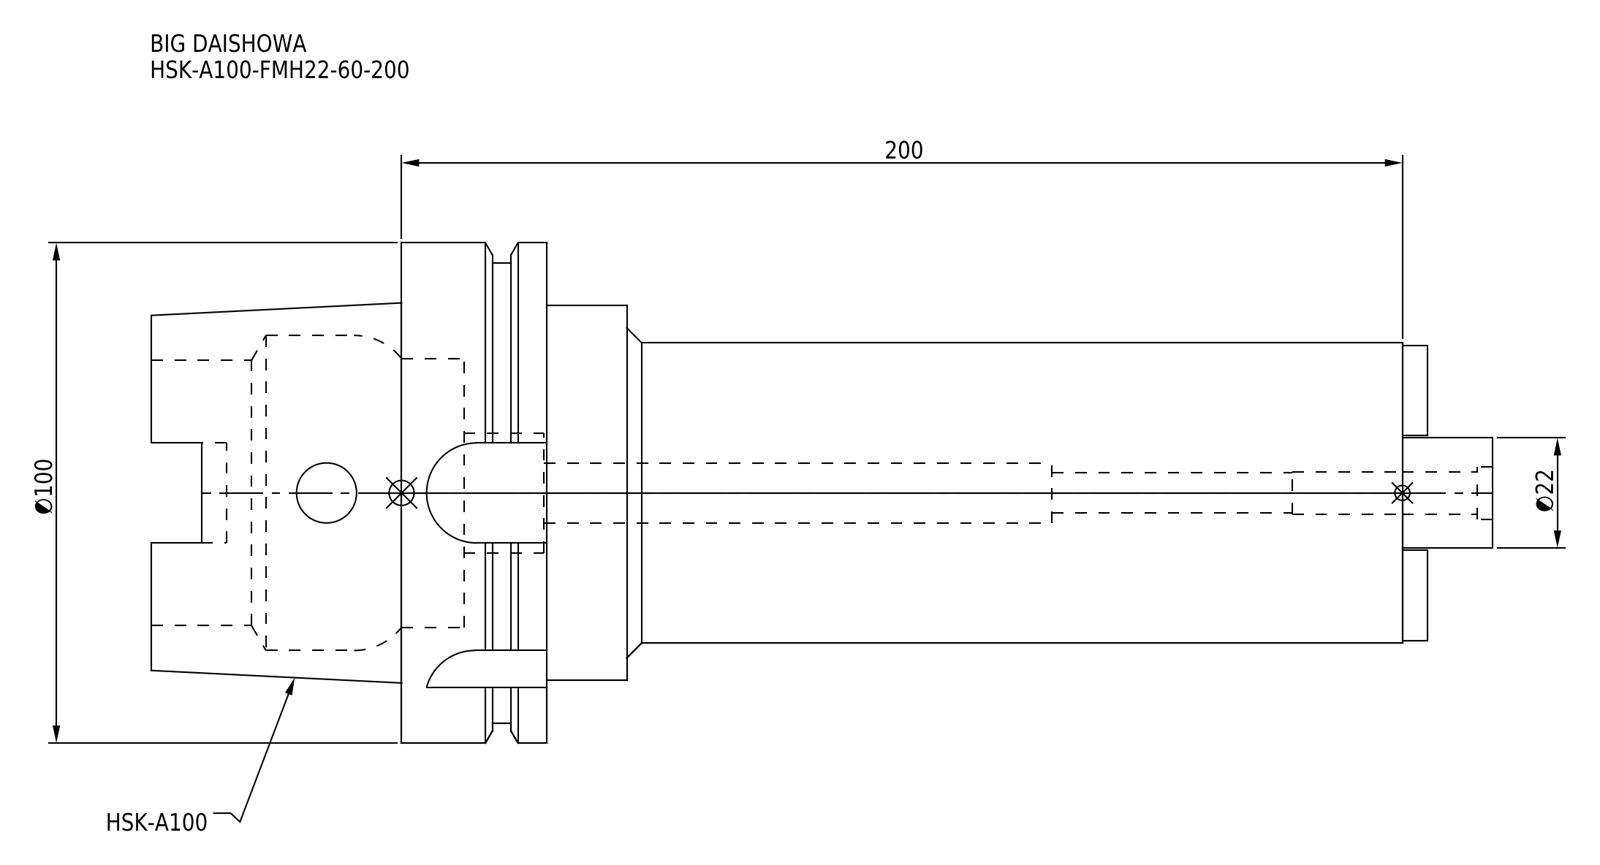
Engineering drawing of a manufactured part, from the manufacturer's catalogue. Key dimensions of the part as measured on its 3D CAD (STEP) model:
Part name (STEP PRODUCT): HSK-A100-FMH22-60-200
STEP written by: CREO PARAMETRIC BY PTC INC, 2016380 (AUTOMOTIVE_DESIGN)
Units: millimetres
Bodies: 1 solid, 109 faces (47 planar, 46 cylindrical, 16 other)
Overall size (bounding box): 268 × 100 × 100
Volume: 755 701 mm³ · Surface area: 90 487 mm²
Round holes (diameter × count): ⌀12 ×2, ⌀8 ×1, ⌀8.5 ×1, ⌀10.5 ×1, ⌀24 ×1, ⌀53 ×1, ⌀53.8 ×1, ⌀63 ×1
Round bosses / shafts (diameter × count): ⌀100 ×1, ⌀92 ×1, ⌀75 ×1, ⌀60 ×1, ⌀22 ×1
Partial cylindrical surfaces — rounded edges, fillets, slot ends (radius × count): R4.88 ×4, R10 ×4
Main face-to-face distances: 29, 16.55, 200, 171, 187.55, 12.45, 16, 250, 79, 62.45
